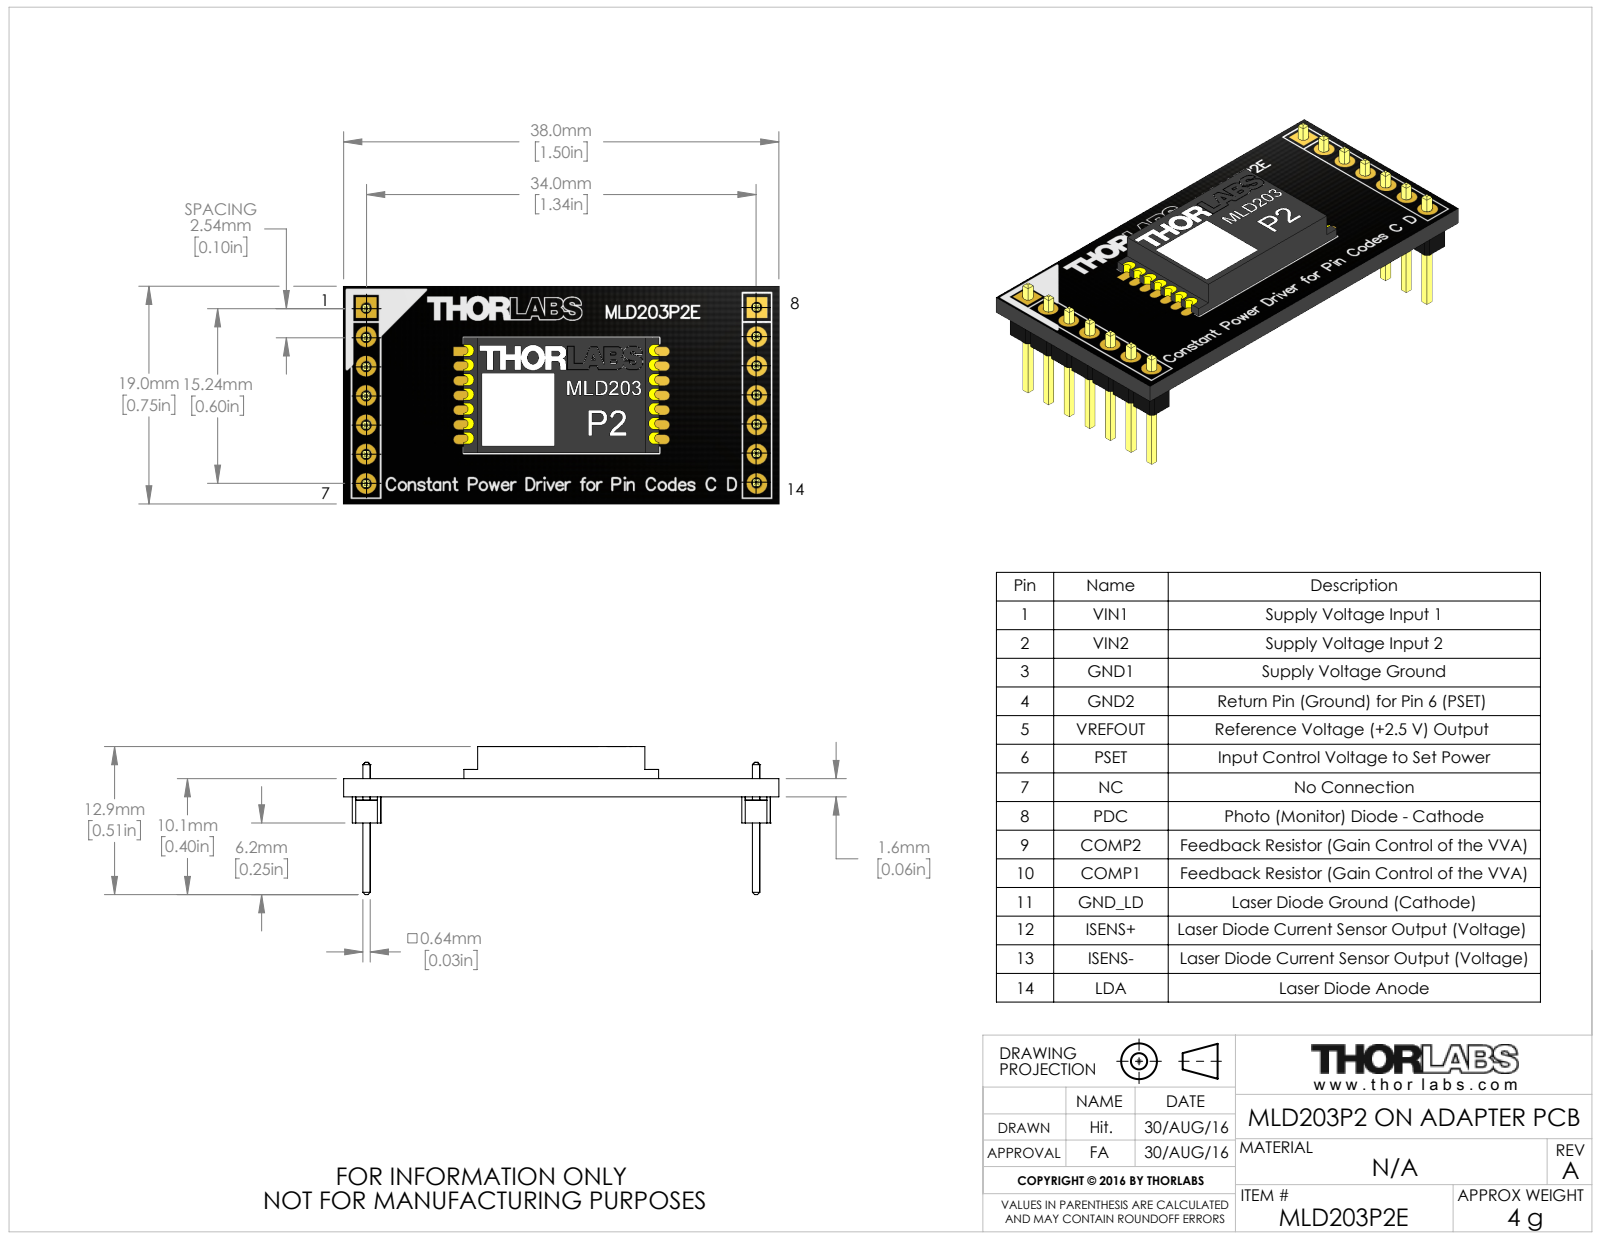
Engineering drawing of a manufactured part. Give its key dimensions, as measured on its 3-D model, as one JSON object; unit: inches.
{"part_name": "MTN006906-E0W", "step_written_by": "SolidWorks 2016 (AUTOMOTIVE_DESIGN)", "units": "inches", "bodies": {"solids": 30, "faces": 1122, "planar": 974, "cylindrical": 84, "other": 64}, "overall_size": [1.496, 0.748, 0.509], "volume_in3": 0.109, "surface_area_in2": 4.81, "round_holes": [[0.035, 14]], "partial_cylinders_radius": [[0.015, 14], [0.021, 14]], "face_to_face_distances": [0.063, 1.339, 0.025, 0.173, 0.11, 0.09, 0.571, 0.177, 0.152, 0.263], "hole_center_spacings": [0.1, 0.2, 0.3, 1.339, 0.4, 1.343, 1.343, 1.353]}
